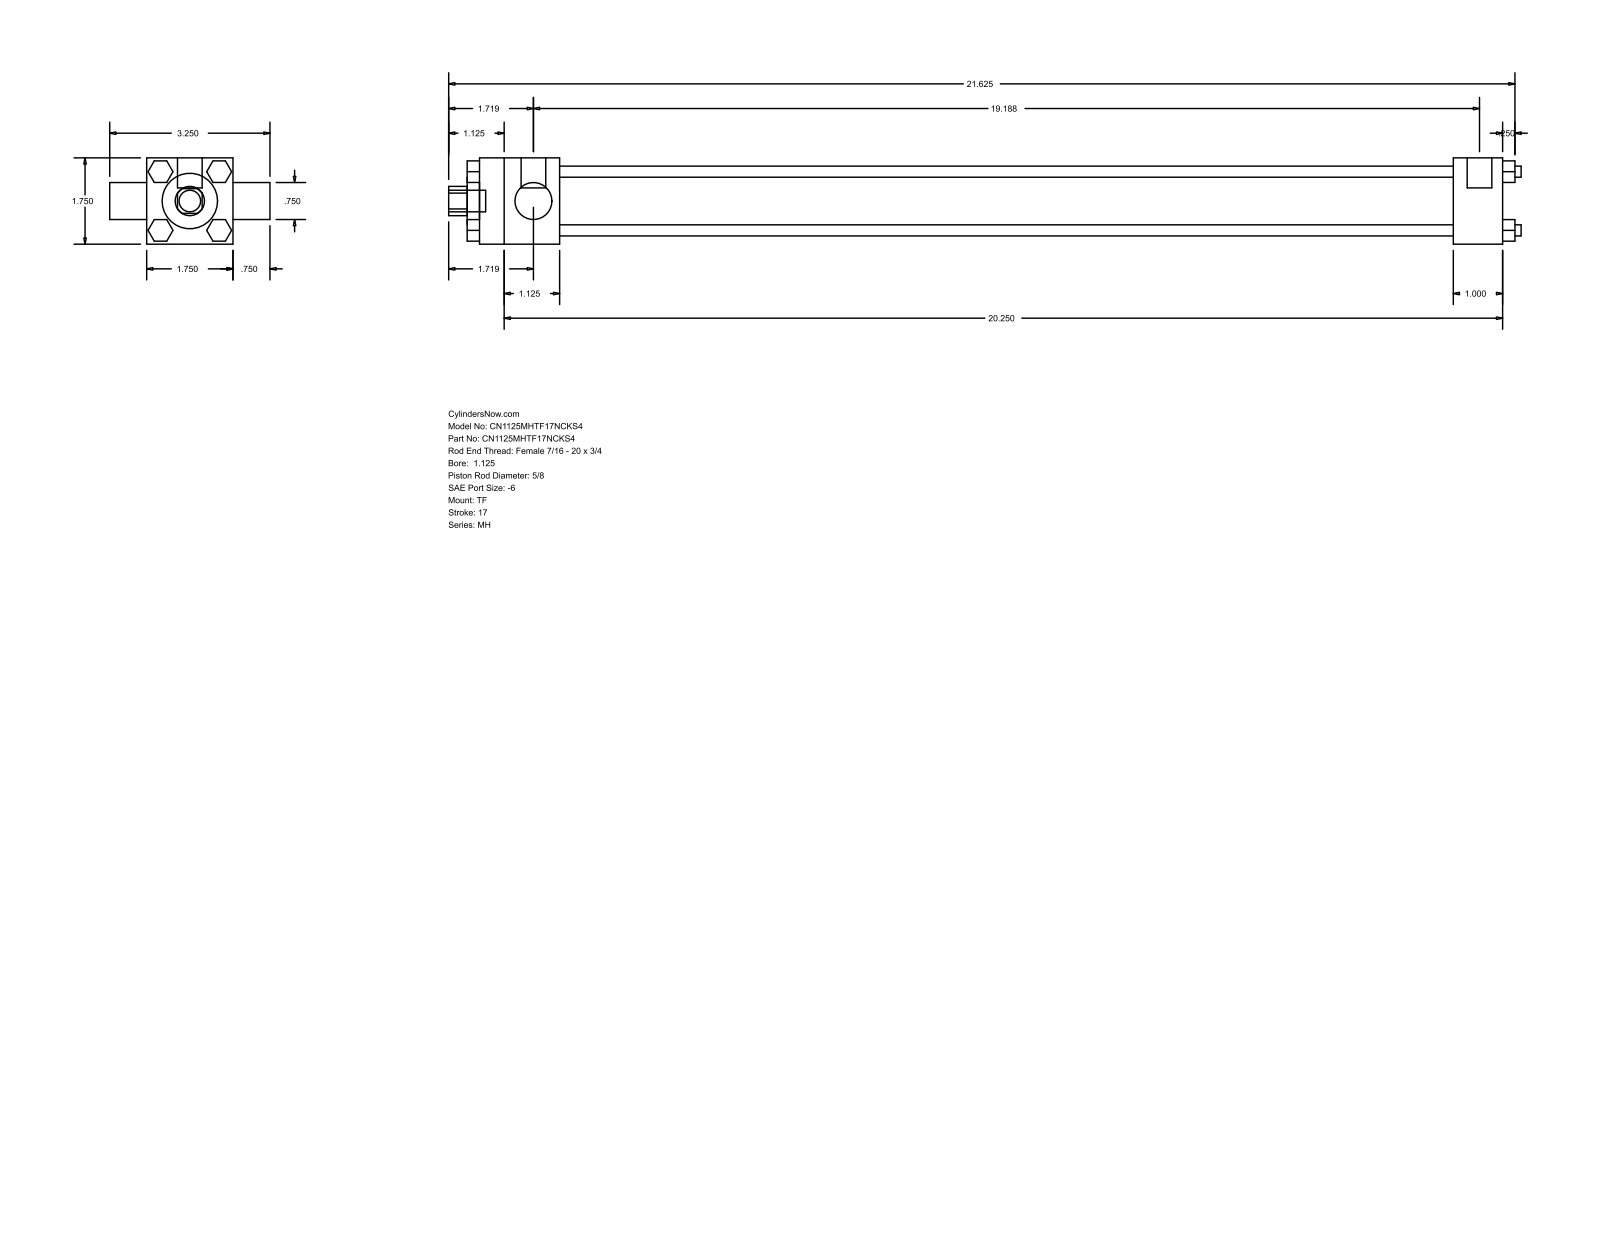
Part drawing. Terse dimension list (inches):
name: MH_TF__0112_0.625
written by: GSSL Pune (CONFIG_CONTROL_DESIGN)
unit: in
bodies: 0 solids, 120 faces (92 planar, 28 cylindrical, 0 other)
size: 21.75 × 3.25 × 1.75
holes: 1× ⌀0.625, 1× ⌀0.75, 1× ⌀1.125, 1× ⌀1.375
bosses: 4× ⌀0.225, 3× ⌀0.219, 2× ⌀0.5, 1× ⌀0.437
rounds: 1× R0.297
face distances: 1.75, 0.25, 21, 0.437, 18.125, 19.125, 1, 1.625, 19.75, 20.75
